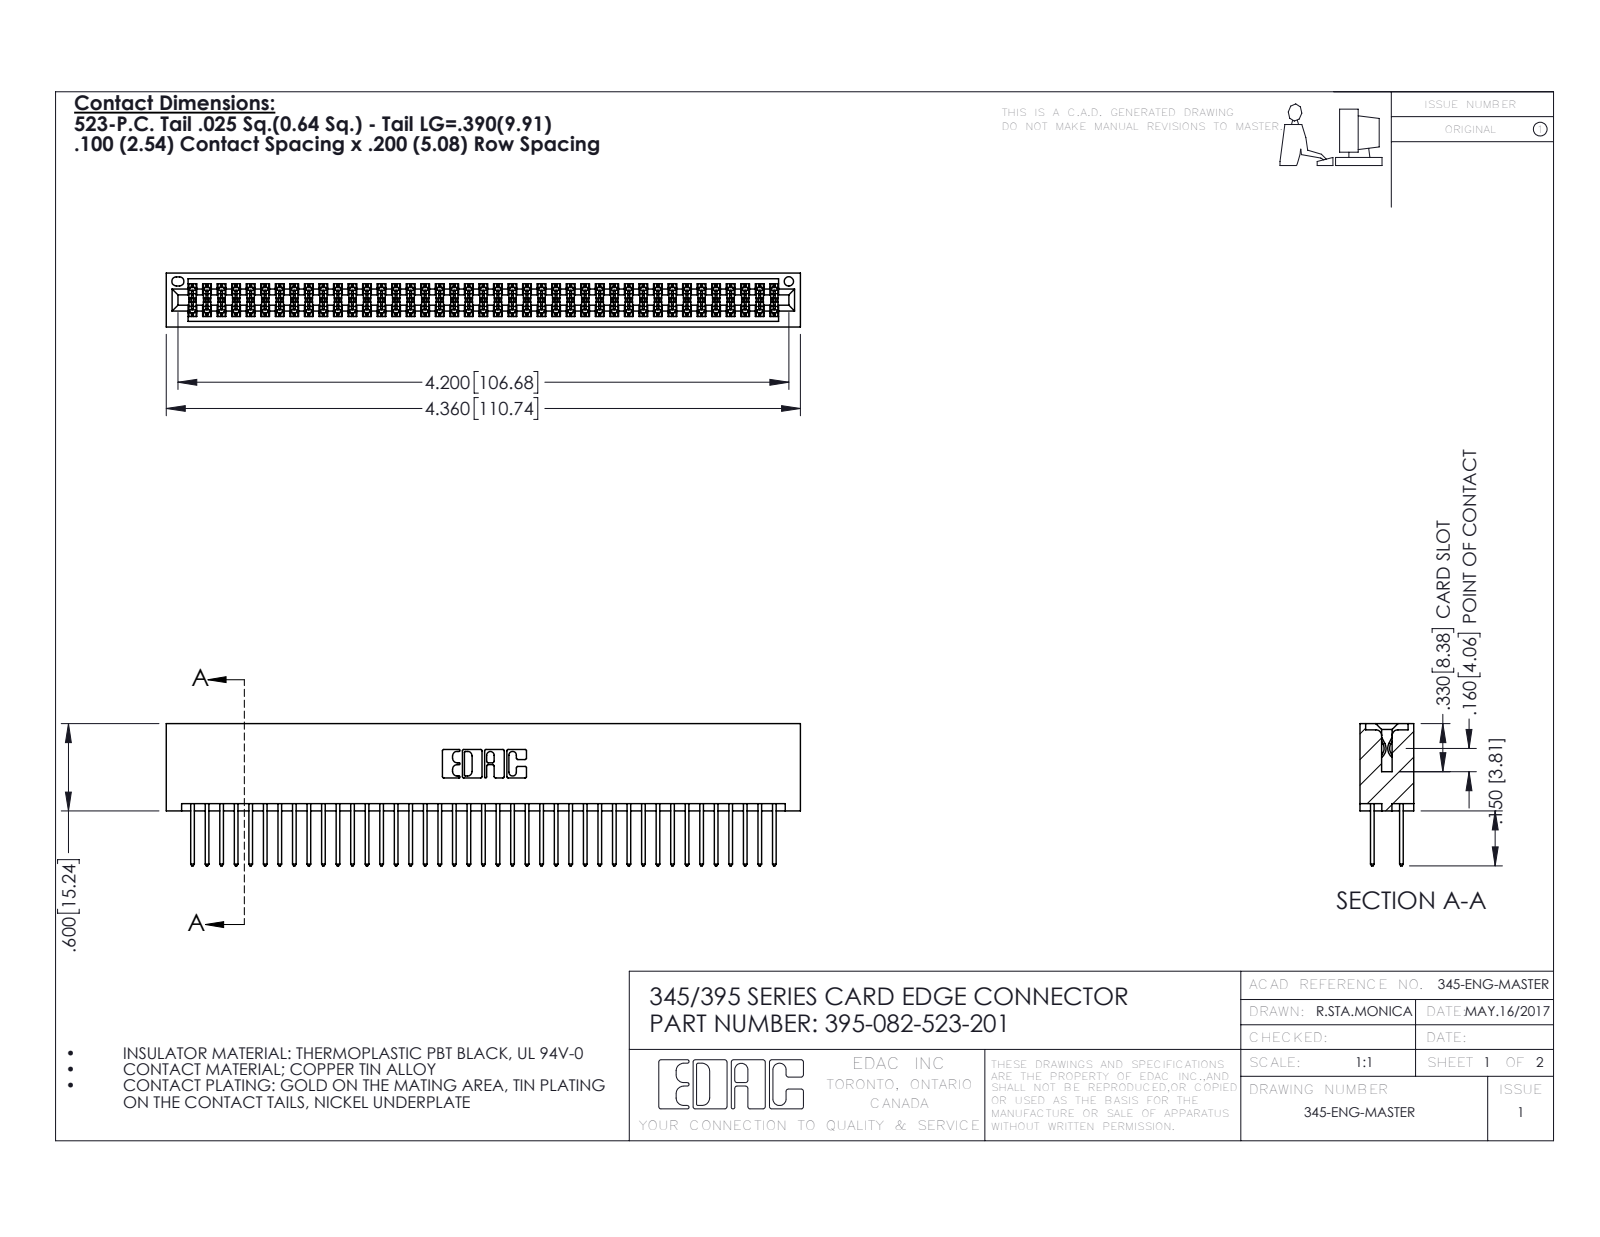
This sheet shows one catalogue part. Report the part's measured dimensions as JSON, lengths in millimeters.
{"part_name": "395-082-523-201; 345-292-001_345-293-123; 345 Part_No Mounting Lugs", "step_written_by": "SolidWorks 2016 (CONFIG_CONTROL_DESIGN)", "units": "millimeters", "bodies": {"solids": 83, "faces": 4218, "planar": 2782, "cylindrical": 1436, "other": 0}, "overall_size": [110.7, 24.8, 9.4], "volume_mm3": 11500, "surface_area_mm2": 18080, "round_holes": [[1.6, 1]], "partial_cylinders_radius": [[0.2, 123], [0.3, 82], [0.3, 22], [0.2, 6], [0.8, 6], [0.7, 3], [0.4, 2], [0.5, 2]], "face_to_face_distances": [7.6, 1.8, 5.1, 2.5, 6.9, 0.6, 9.4, 5.7, 4.4, 3.8]}
